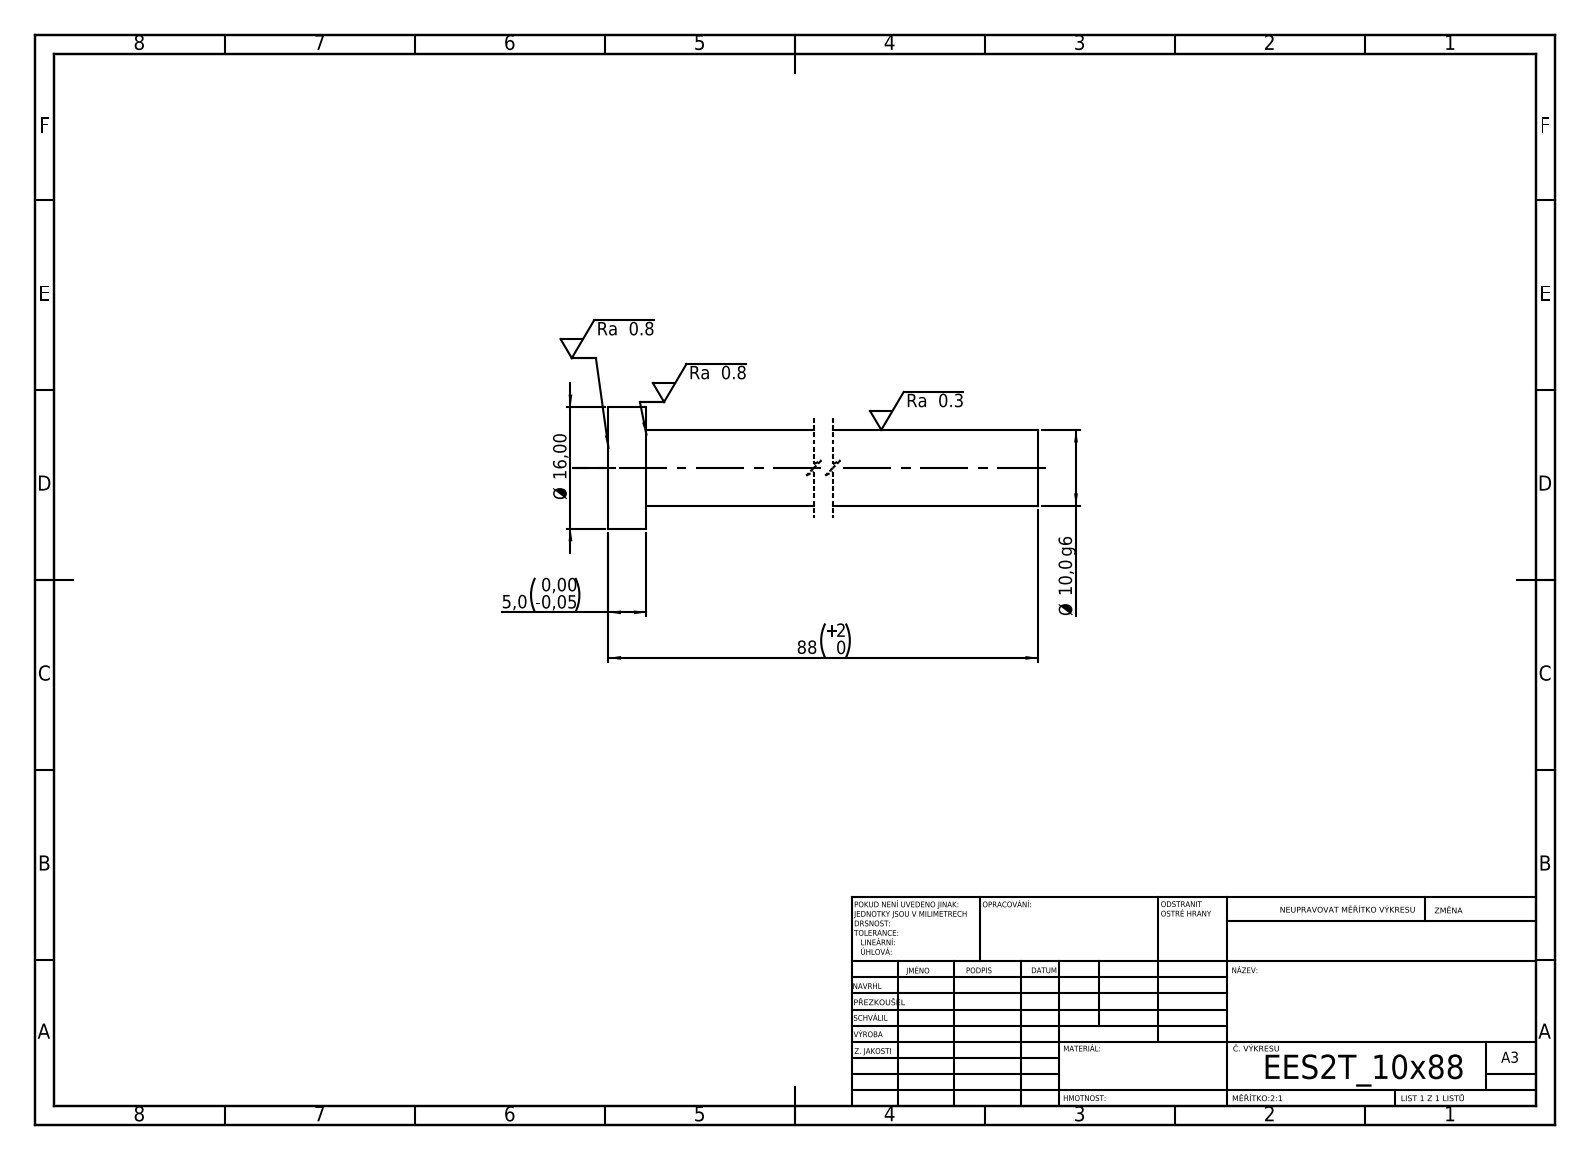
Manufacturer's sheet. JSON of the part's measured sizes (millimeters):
{"step_written_by": "SolidWorks 2019 (CONFIG_CONTROL_DESIGN)", "units": "millimeters", "bodies": {"solids": 1, "faces": 7, "planar": 3, "cylindrical": 4, "other": 0}, "overall_size": [88, 16, 16], "volume_mm3": 7524, "surface_area_mm2": 3261, "round_bosses_or_shafts": [[16, 1], [10, 1]], "face_to_face_distances": [5, 88, 83]}
